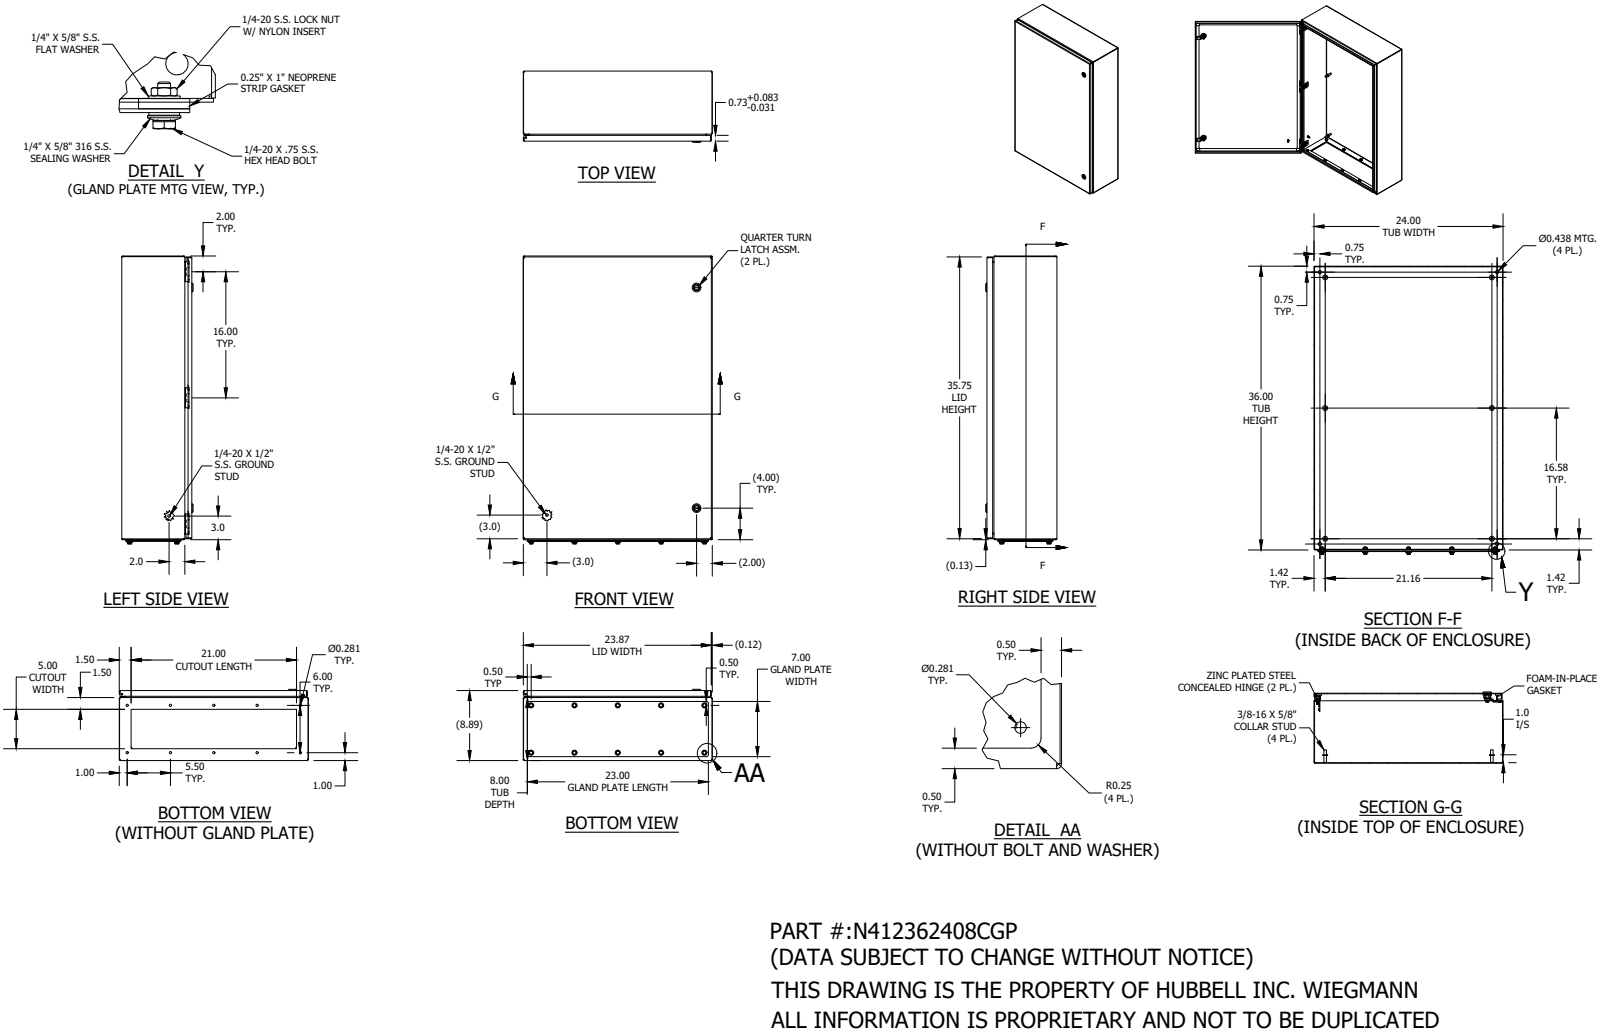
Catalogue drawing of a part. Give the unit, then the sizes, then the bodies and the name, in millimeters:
Units: millimetres
Overall size (bounding box): 927.6 × 609.6 × 229.7
Round holes (diameter × count): ⌀4.1 ×12, ⌀5.4 ×10, ⌀7.1 ×10, ⌀7.4 ×10, ⌀8.9 ×9, ⌀4.8 ×7, ⌀7 ×7, ⌀2.4 ×6, ⌀4.2 ×6, ⌀6 ×6, ⌀6 ×4, ⌀11.1 ×4
Round bosses / shafts (diameter × count): ⌀6.4 ×24, ⌀15.9 ×15, ⌀16.5 ×10, ⌀15.2 ×10, ⌀11.1 ×10, ⌀9.1 ×6, ⌀8.4 ×6, ⌀8.1 ×6
Partial cylindrical surfaces — rounded edges, fillets, slot ends (radius × count): R0.3 ×56, R1.3 ×38, R0.5 ×21, R1.2 ×20, R3.1 ×20, R3.2 ×12, R3.3 ×12, R4 ×9
Main face-to-face distances: 1.9, 223.8, 221.9, 225.7, 1.9, 607.7, 917.7, 605.8, 609.6, 915.8
Hole centre spacings: 139.7, 152.4, 406.4, 279.4, 206.7, 16.8, 318.3, 406.5
Volume: 4 162 000 mm³ · Surface area: 4 122 000 mm²
Bodies: 99 solids, 3003 faces (1165 planar, 952 cylindrical, 886 other)
Part name (STEP PRODUCT): N412362408CGP
STEP written by: SolidWorks 2019 (AUTOMOTIVE_DESIGN)
